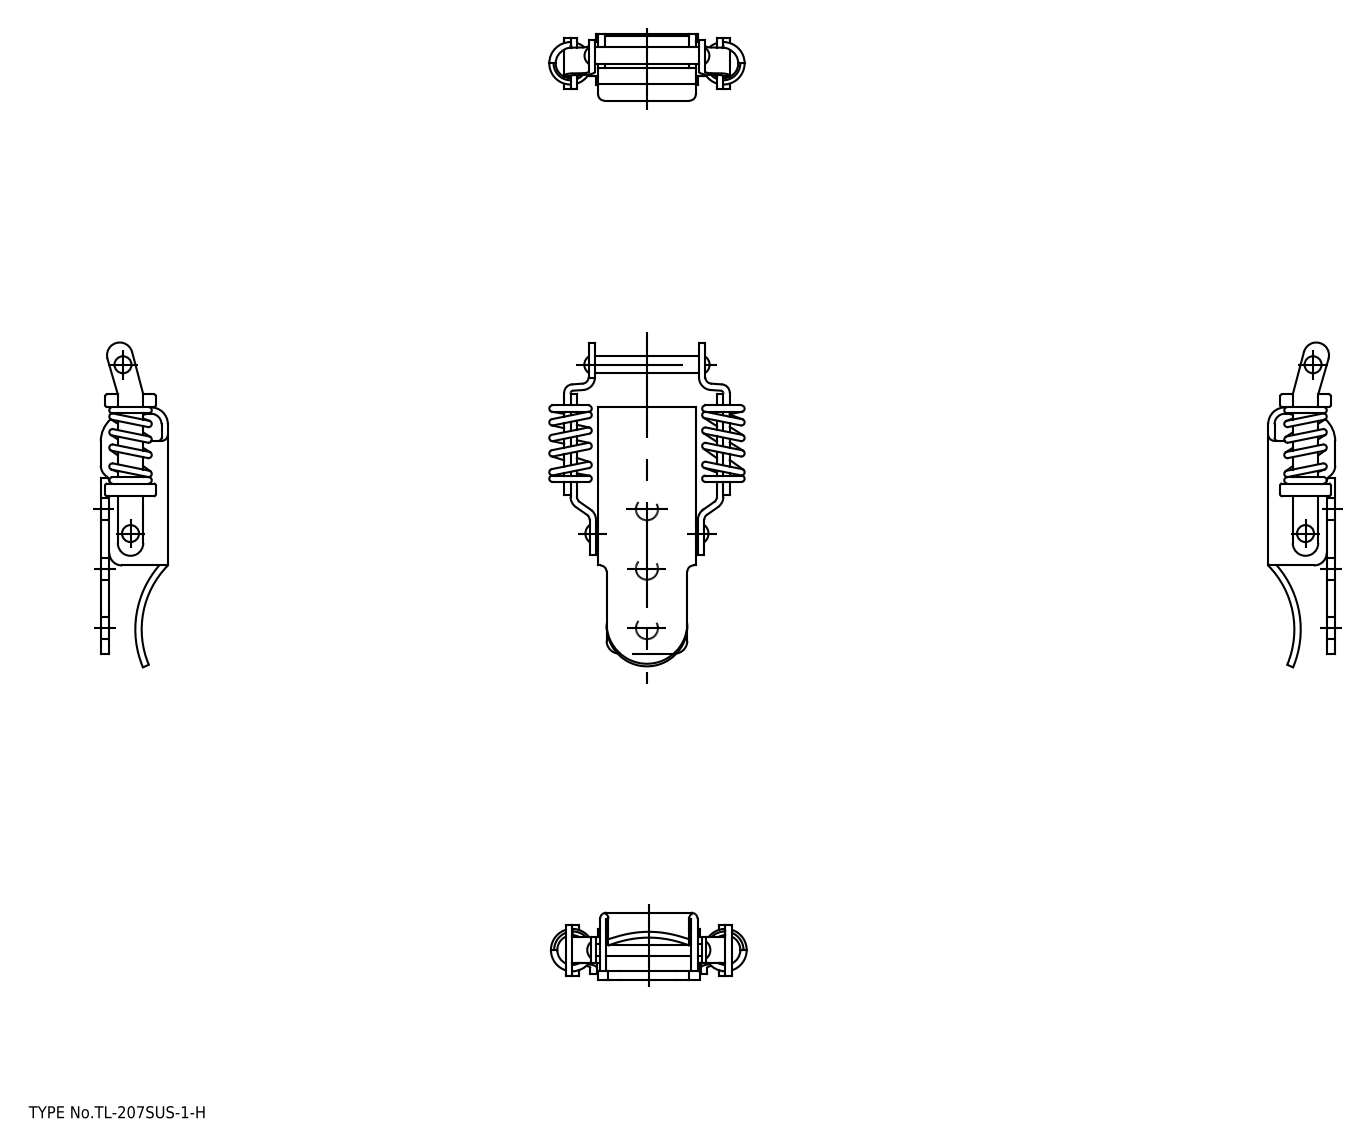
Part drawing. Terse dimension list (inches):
name: spring; armA; armB; lever (+1 more)
written by: spGate 19.8.4 (****-****-****-****) (AUTOMOTIVE_DESIGN)
unit: in
bodies: 6 solids, 219 faces (107 planar, 80 cylindrical, 32 other)
size: 3.012 × 1.811 × 0.622
volume: 0.501 in³; area: 18.83 in²
holes: 3× ⌀0.205, 1× ⌀0.157
bosses: 1× ⌀0.157, 1× ⌀0.118
rounds: 14× R0.059, 12× R0.118, 9× R0.02, 5× R0.079, 2× R0.026, 1× R0.098, 1× R0.138, 1× R0.157
face distances: 0.059, 0.079, 0.315, 0.256, 1.102, 1.161, 0.846, 0.484, 0.563, 0.543
hole spacings: 0.551, 1.102
